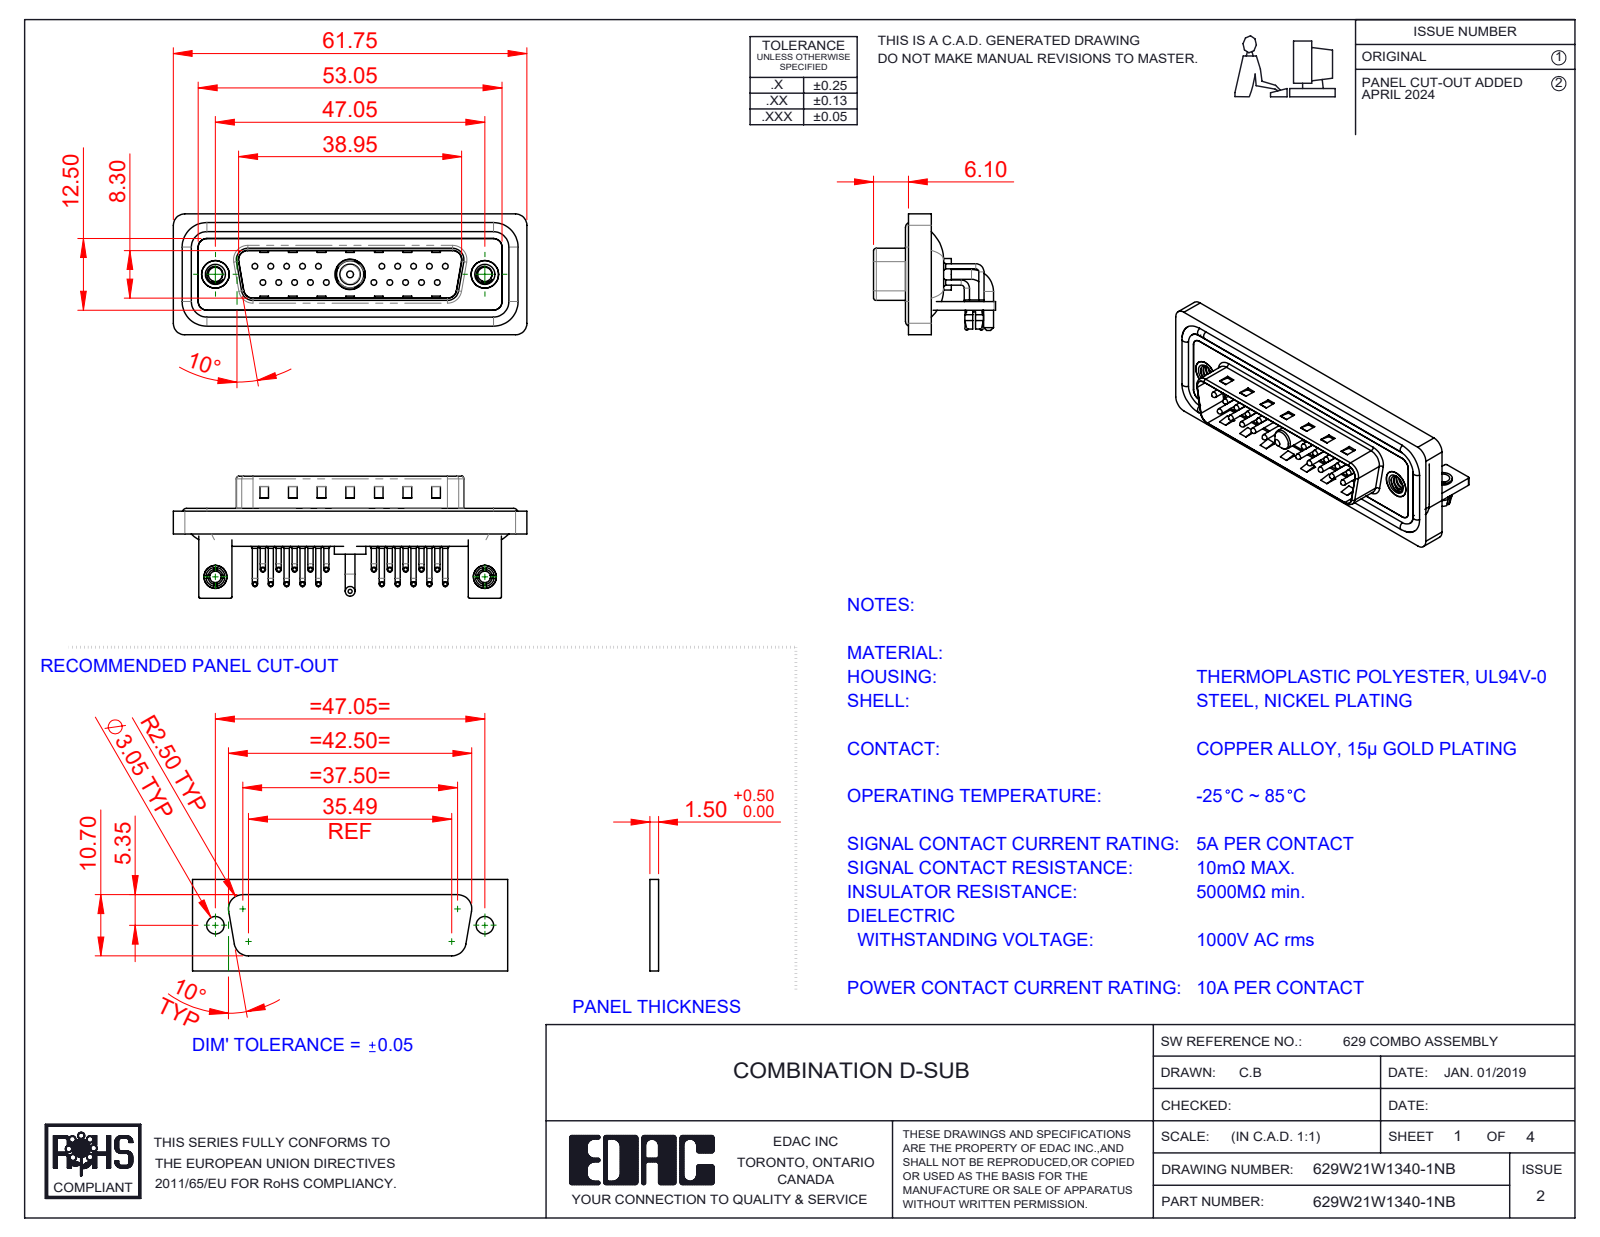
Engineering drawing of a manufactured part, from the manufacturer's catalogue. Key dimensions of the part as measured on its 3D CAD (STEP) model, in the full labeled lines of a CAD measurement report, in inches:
Part name (STEP PRODUCT): Power Pin_10A RA; 629Combo Contact Row 1; 629Combo Contact Row 2; 629Combo Stabilizer Bracket (+7 more)
STEP written by: SolidWorks 2023 (CONFIG_CONTROL_DESIGN)
Units: inches
Bodies: 33 solids, 2856 faces (1567 planar, 979 cylindrical, 310 other)
Overall size (bounding box): 2.431 × 0.839 × 0.831
Volume: 0.468 in³ · Surface area: 20.88 in²
Round holes (diameter × count): ⌀0.079 ×22, ⌀0.03 ×20, ⌀0.063 ×20, ⌀0.098 ×4, ⌀0.126 ×2, ⌀0.157 ×2, ⌀0.189 ×2, ⌀0.197 ×2, ⌀0.191 ×1, ⌀0.209 ×1
Round bosses / shafts (diameter × count): ⌀0.035 ×40, ⌀0.059 ×20, ⌀0.039 ×20, ⌀0.026 ×20, ⌀0.063 ×4, ⌀0.193 ×2, ⌀0.157 ×2, ⌀0.134 ×2
Partial cylindrical surfaces — rounded edges, fillets, slot ends (radius × count): R0.04 ×20, R0.079 ×19, R0.059 ×18, R0.01 ×16, R0.02 ×9, R0.063 ×8, R0.024 ×4, R0.026 ×4
Main face-to-face distances: 0.016, 0.031, 0.083, 0.114, 0.059, 0.043, 0.161, 0.063, 0.177, 0.146
Hole centre spacings: 0.124, 0.109, 0.218, 0.327, 0.198, 0.763, 0.826, 0.872
